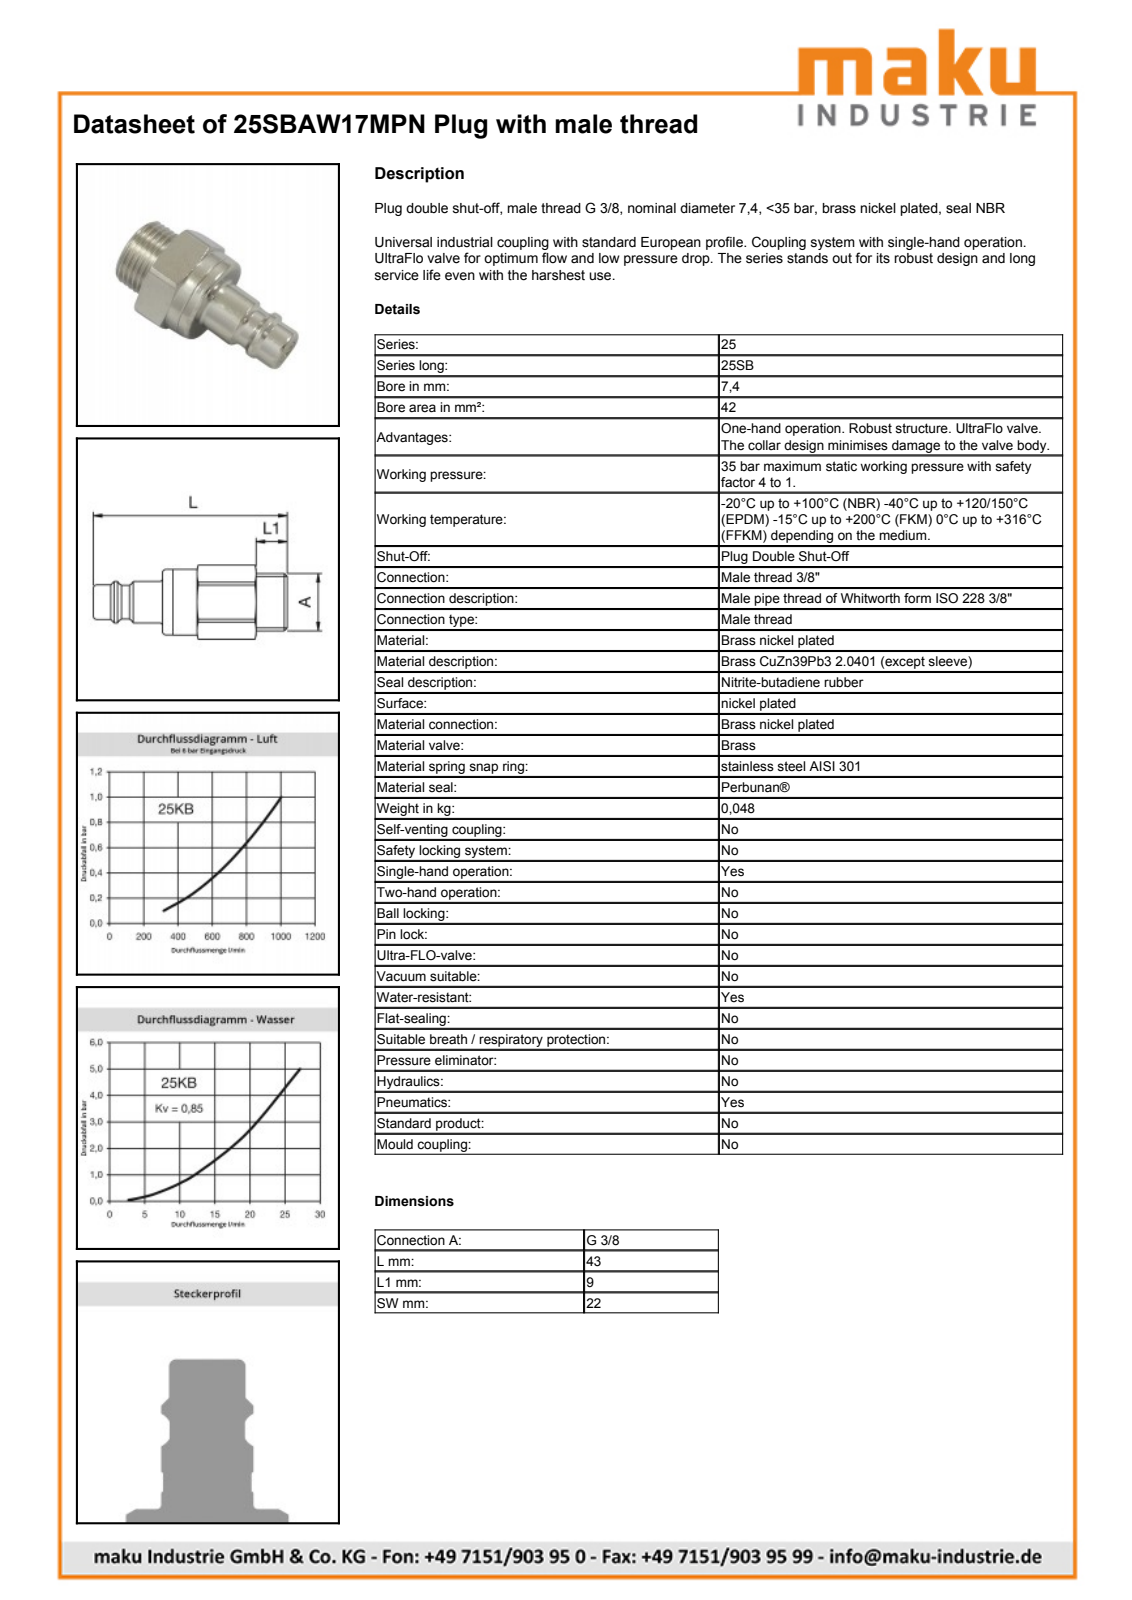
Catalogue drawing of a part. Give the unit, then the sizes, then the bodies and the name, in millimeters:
Units: millimetres
Overall size (bounding box): 43.1 × 24.49 × 23.86
Round holes (diameter × count): ⌀14.45 ×1, ⌀17 ×1
Round bosses / shafts (diameter × count): ⌀21 ×1, ⌀16.67 ×1, ⌀16.5 ×1, ⌀13.32 ×1, ⌀12 ×1, ⌀10 ×1, ⌀9.75 ×1
Partial cylindrical surfaces — rounded edges, fillets, slot ends (radius × count): R12.4 ×1
Main face-to-face distances: 9, 22, 14.1, 23.1, 21.98, 4.5, 7.5, 11.1, 6.6, 15.6
Volume: 9 001 mm³ · Surface area: 3 850 mm²
Bodies: 1 solid, 58 faces (17 planar, 17 cylindrical, 24 other)
Part name (STEP PRODUCT): D107650
STEP written by: Autodesk Inventor 2013 (AUTOMOTIVE_DESIGN)
